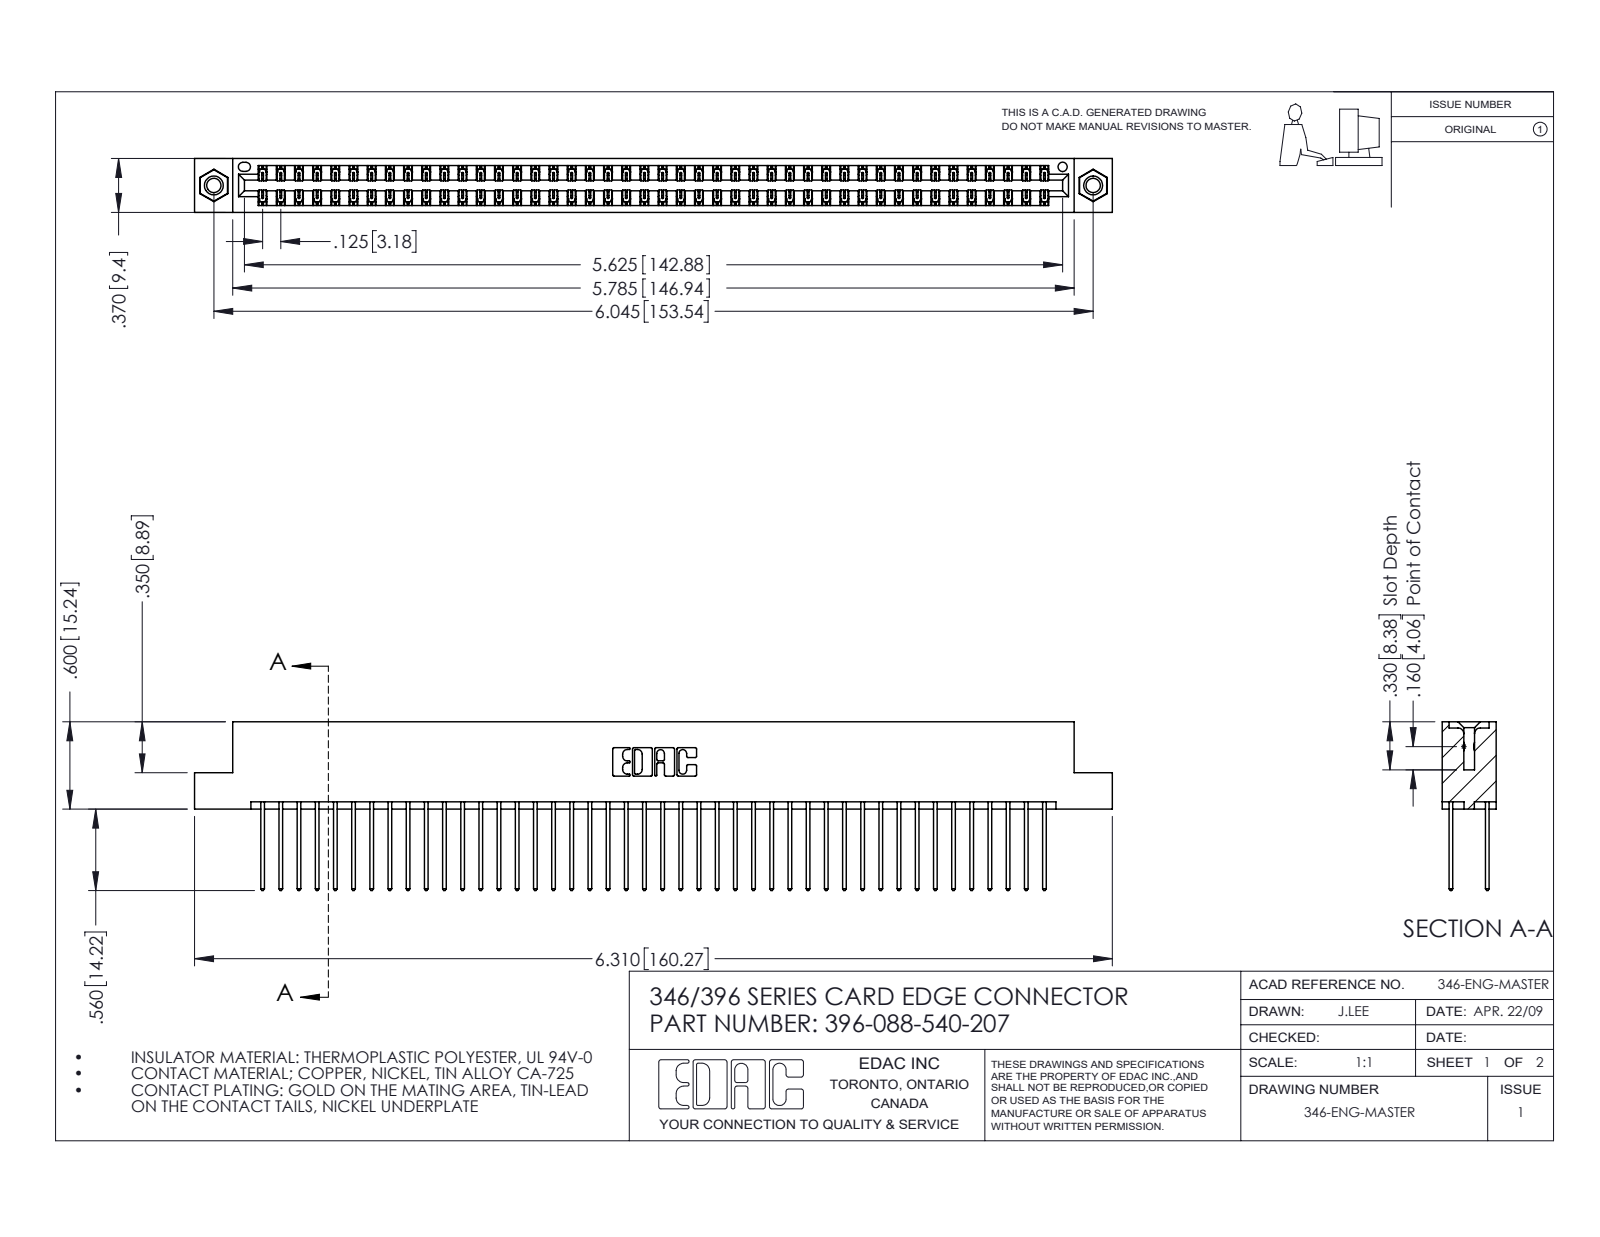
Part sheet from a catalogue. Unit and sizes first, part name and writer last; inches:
Units: inches
Overall size (bounding box): 6.31 × 1.16 × 0.37
Round holes (diameter × count): ⌀0.098 ×2, ⌀0.125 ×2, ⌀0.156 ×2, ⌀0.064 ×1
Round bosses / shafts (diameter × count): ⌀0.155 ×2
Partial cylindrical surfaces — rounded edges, fillets, slot ends (radius × count): R0.006 ×132, R0.01 ×88, R0.01 ×22, R0.007 ×6, R0.031 ×6, R0.026 ×3, R0.014 ×2, R0.022 ×2
Main face-to-face distances: 0.048, 0.322, 0.25, 0.072, 0.298, 0.025, 0.37, 0.275, 0.148, 0.222
Hole centre spacings: 0.246, 5.836, 6.045
Volume: 0.974 in³ · Surface area: 36.56 in²
Bodies: 91 solids, 4758 faces (3188 planar, 1554 cylindrical, 16 other)
Part name (STEP PRODUCT): 345-250-001_345-250-005-103; 345-292-001_345-293-140; 346 Part_Flush Mounting Lugs - 0.156 Dia-TI; 396-088-540-207
STEP written by: SolidWorks 2016 (CONFIG_CONTROL_DESIGN)
